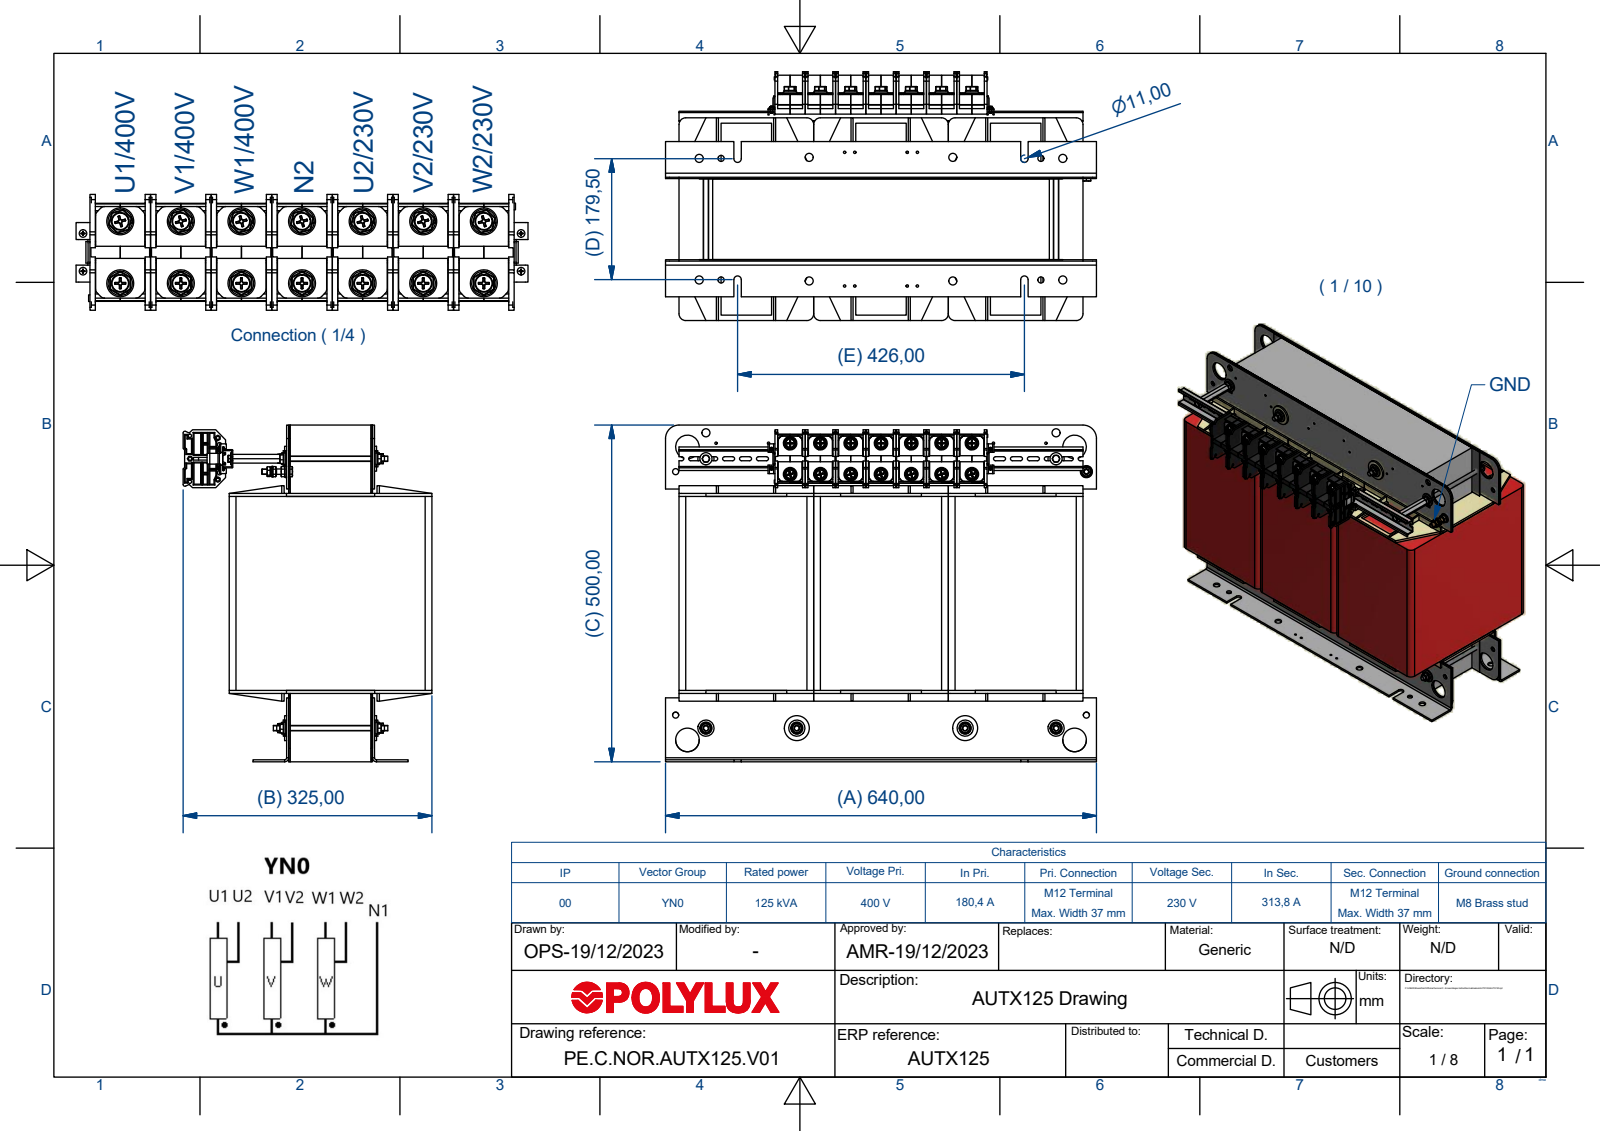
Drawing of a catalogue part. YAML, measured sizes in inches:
part_name: "AUTX125"
step_written_by: "Autodesk Inventor 2018 (AUTOMOTIVE_DESIGN)"
units: inches
bodies: {solids: 149, faces: 8568, planar: 6328, cylindrical: 1517, other: 723}
overall_size: [25.197, 19.685, 14.545]
volume: 4109
surface_area: 9379
round_holes:
  - {diameter: 0.472, count: 22}
  - {diameter: 0.177, count: 20}
  - {diameter: 0.138, count: 18}
  - {diameter: 0.335, count: 15}
  - {diameter: 0.413, count: 14}
  - {diameter: 0.421, count: 14}
  - {diameter: 0.482, count: 14}
  - {diameter: 0.354, count: 10}
  - {diameter: 0.453, count: 10}
  - {diameter: 0.262, count: 9}
  - {diameter: 0.331, count: 9}
  - {diameter: 1.378, count: 6}
round_bosses_or_shafts:
  - {diameter: 0.787, count: 14}
  - {diameter: 0.713, count: 14}
  - {diameter: 0.388, count: 14}
  - {diameter: 0.315, count: 9}
  - {diameter: 0.945, count: 8}
  - {diameter: 1.457, count: 4}
  - {diameter: 0.154, count: 4}
  - {diameter: 0.118, count: 4}
partial_cylinders:
  - {radius: 0.02, count: 142}
  - {radius: 0.039, count: 74}
  - {radius: 0.157, count: 56}
  - {radius: 0.118, count: 50}
  - {radius: 0.061, count: 44}
  - {radius: 0.197, count: 20}
  - {radius: 0.037, count: 14}
  - {radius: 0.01, count: 12}
face_to_face_distances: [7.874, 0.157, 4.941, 0.207, 0.089, 4.813, 0.079, 4.823, 4.734, 15.748]
hole_center_spacings: [13.131, 8.11, 3.071, 3.733, 9.843, 16.621, 0.591, 0.938]
